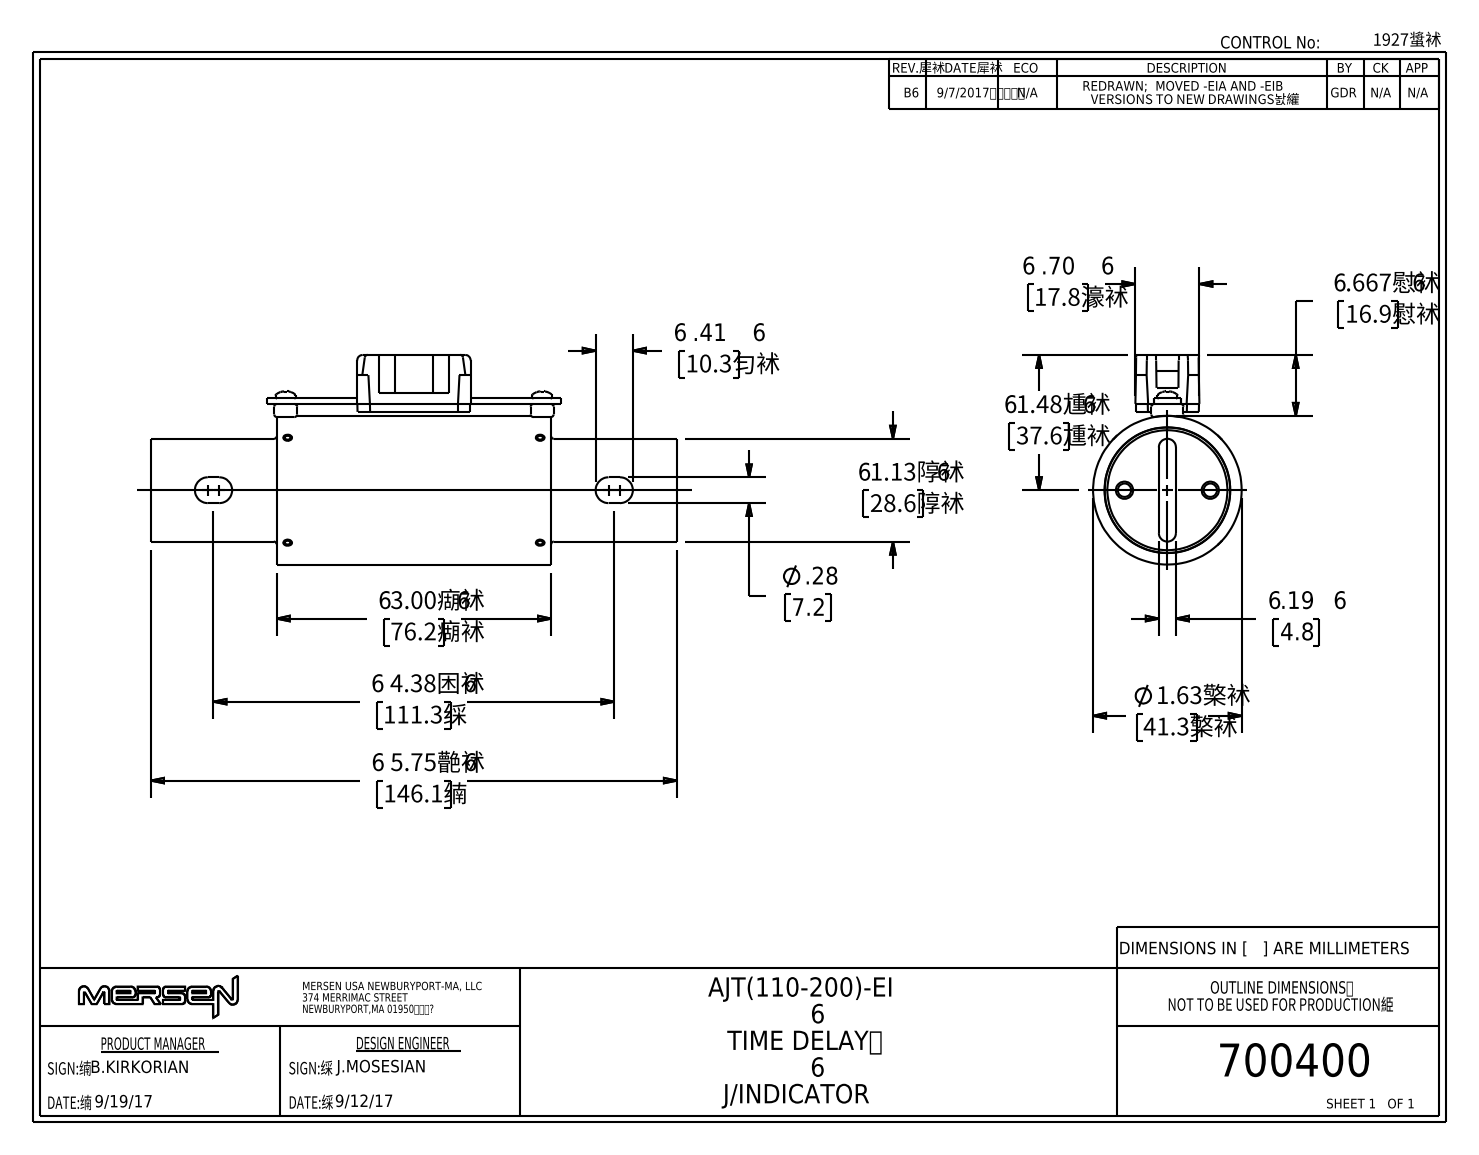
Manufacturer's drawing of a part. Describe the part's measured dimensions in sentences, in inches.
The part is named "700400revB". Its 3-D file was written by "SolidWorks 2016 (AUTOMOTIVE_DESIGN)". It is 26 solids with 1412 faces: 548 planar, 499 cylindrical and 365 other. Overall it measures 5.75 by 2.292 by 1.625 inches. Its volume is 3.4 cubic inches and its surface area 59.65 square inches. Round holes: 4 of diameter 0.095, 3 of diameter 0.17, 2 of diameter 0.113, 2 of diameter 0.146, 2 of diameter 0.188, 1 of diameter 0.125, 1 of diameter 0.125, 1 of diameter 1.375. Round bosses or shafts: 4 of diameter 0.094, 2 of diameter 0.219, 2 of diameter 0.192, 2 of diameter 0.112, 2 of diameter 0.08, 1 of diameter 1.625, 1 of diameter 1.372, 1 of diameter 0.365. Partial cylindrical surfaces (rounded edges, fillets, slot ends): 31 of radius 4, 26 of radius 0.03, 14 of radius 0.005, 10 of radius 0.02, 10 of radius 0.06, 4 of radius 0.07, 4 of radius 0.141, 2 of radius 0.08. The main face-to-face distances are 0.187, 0.25, 2.75, 3, 2.5, 0.06, 0.08, 0.139, 0.062, 0.084. The hole center spacings are 0.19, 0.469, 1.212, 1.402, 1.592, 2.76, 0.38, 0.938.
